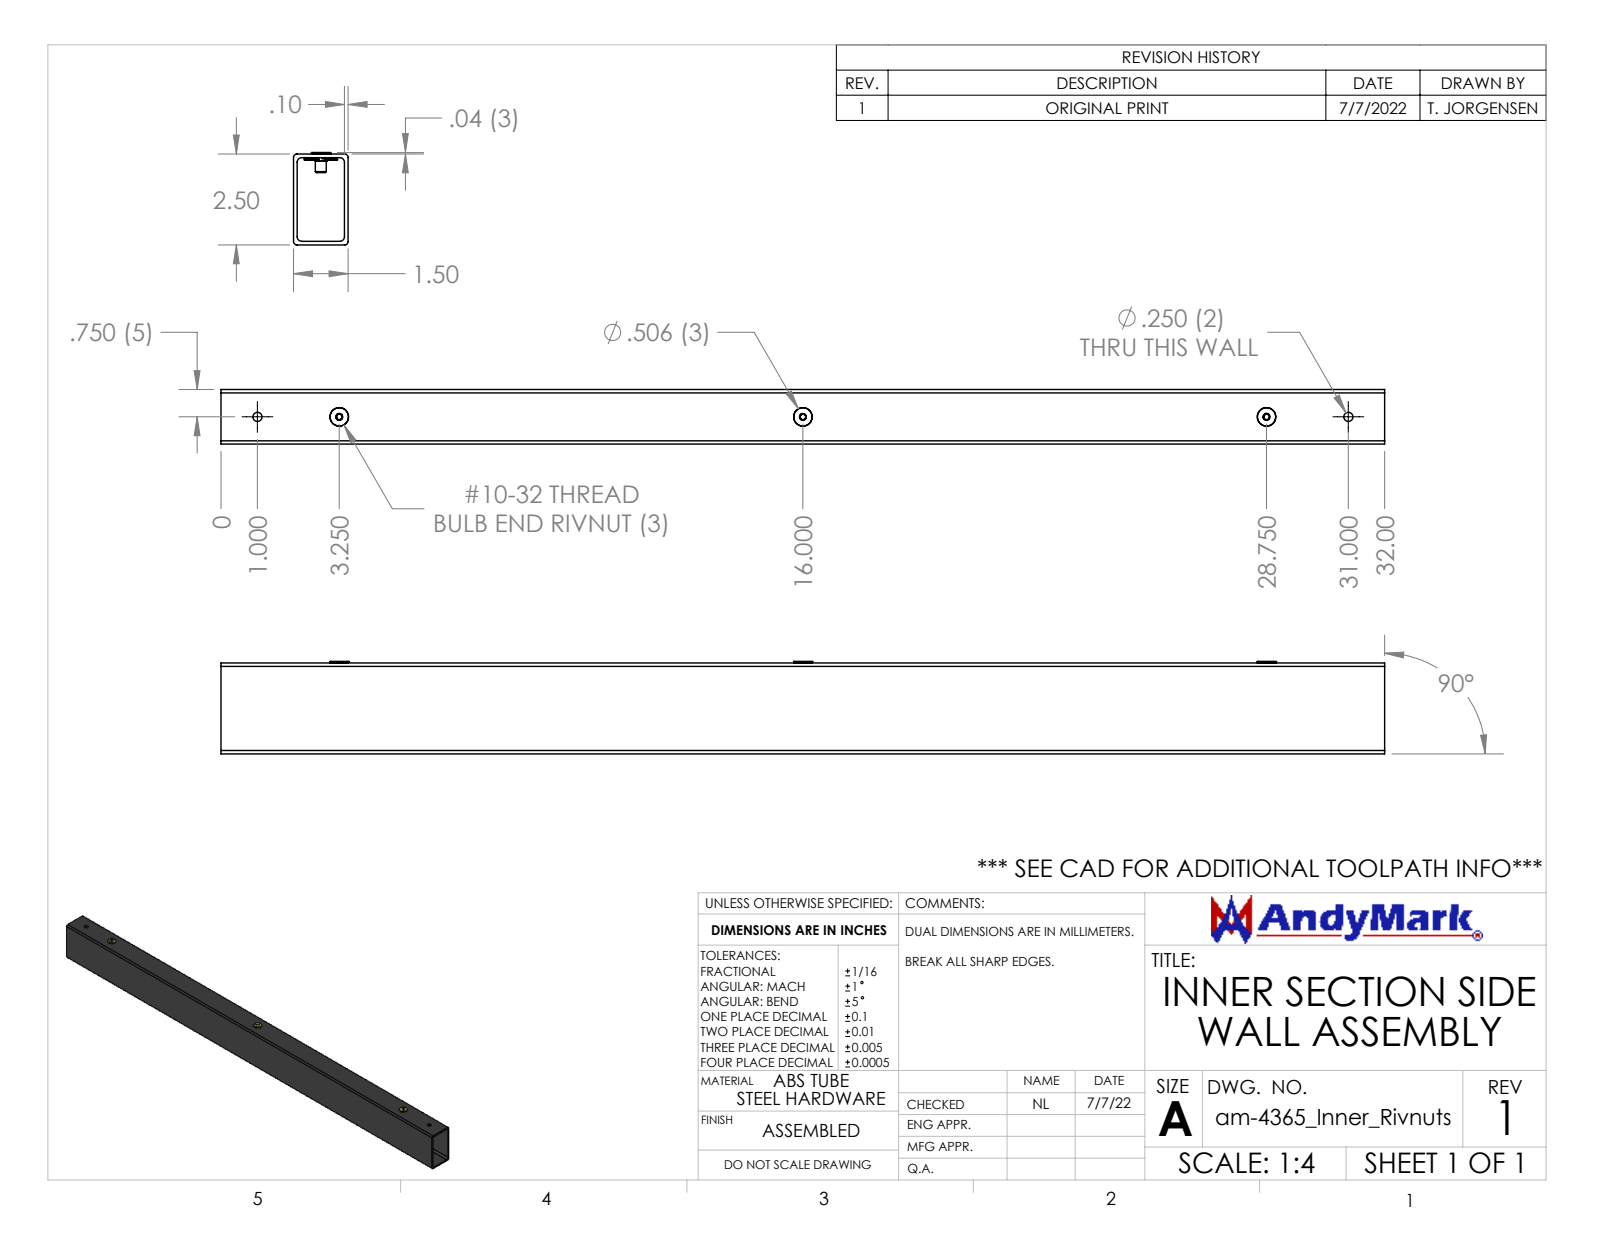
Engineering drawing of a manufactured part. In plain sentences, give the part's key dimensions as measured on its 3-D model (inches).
The part is named "ip-4365_Inner_Drilled Inner Section Wall; am-4365_Inner_Rivnuts Inner Section Wall; am-1577 10-32 RivNut for Plastics_Installed". Its 3-D file was written by "SolidWorks 2022 (CONFIG_CONTROL_DESIGN)". It is 4 solids with 328 faces: 94 planar, 114 cylindrical and 120 other. Overall it measures 32 by 2.538 by 1.5 inches. Its volume is 24.58 cubic inches and its surface area 482.7 square inches. Round holes: 3 of diameter 0.19, 3 of diameter 0.339, 2 of diameter 0.25. Round bosses or shafts: 3 of diameter 0.51, 3 of diameter 0.358, 3 of diameter 0.296. Partial cylindrical surfaces (rounded edges, fillets, slot ends): 4 of radius 0.094, 4 of radius 0.125. The main face-to-face distances are 0.1, 1.4, 1.5, 2.4, 1.3, 2.5, 2.3, 32, 0.038, 0.138. The hole center spacings are 2.25, 12.75, 15, 27.75, 25.5, 30.
